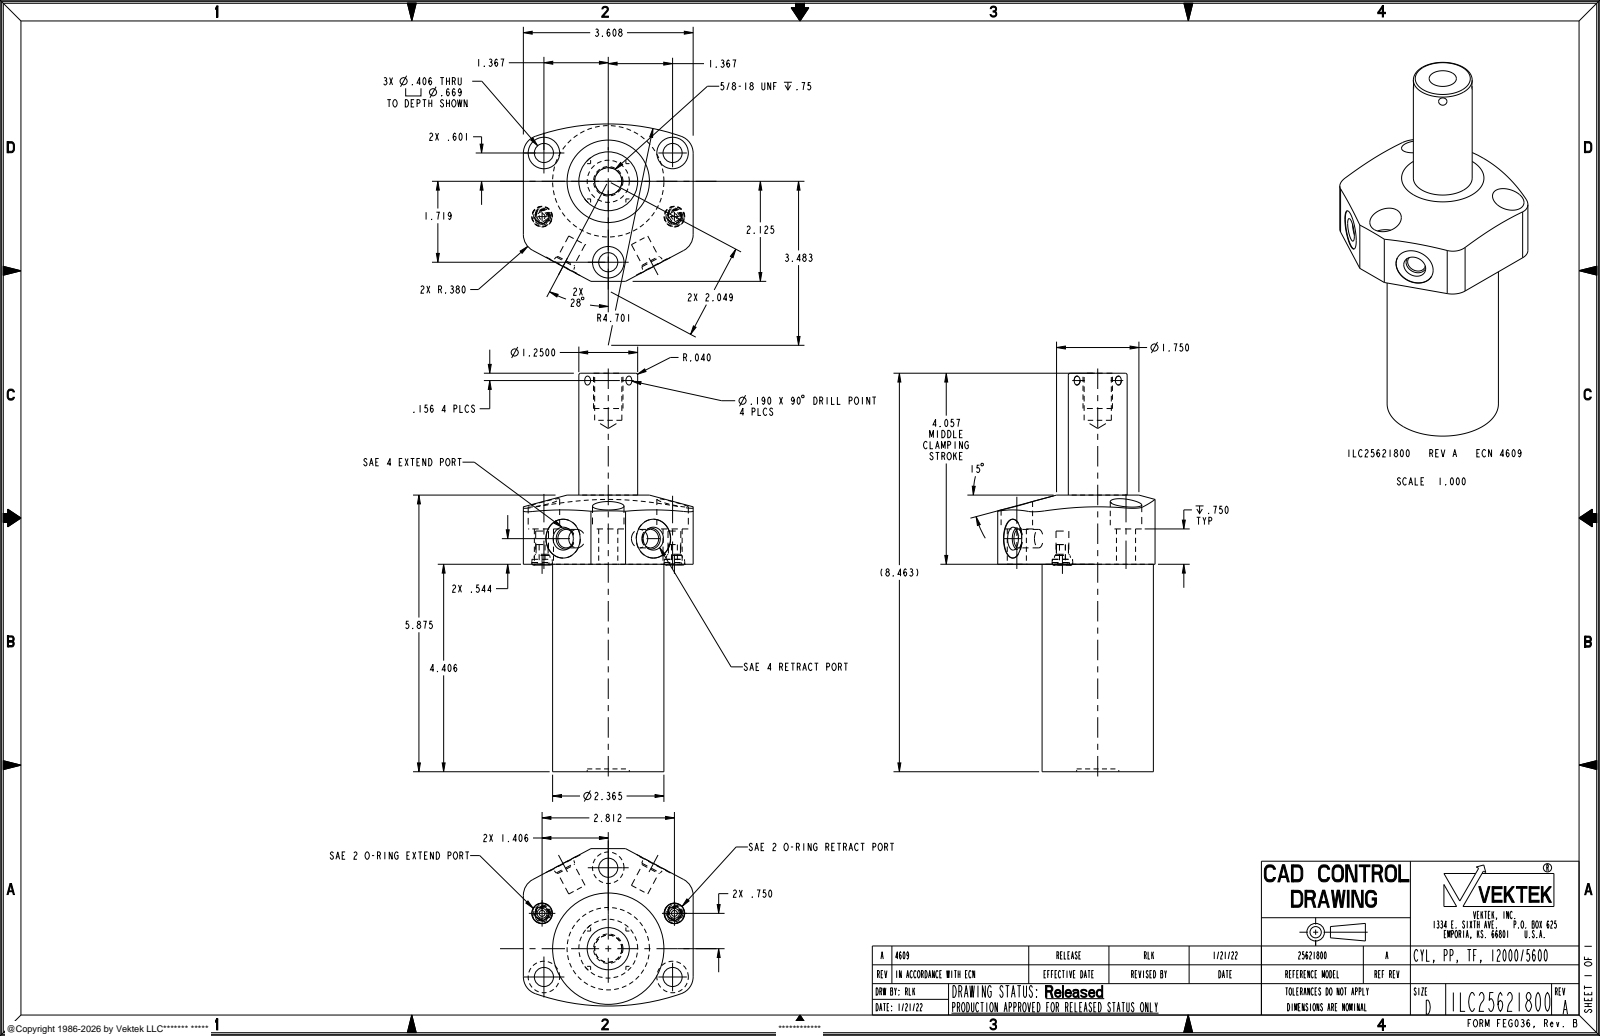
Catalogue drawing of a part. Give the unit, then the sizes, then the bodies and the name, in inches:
Units: inches
Overall size (bounding box): 8.463 × 3.808 × 3.543
Round holes (diameter × count): ⌀0.406 ×3, ⌀0.669 ×3, ⌀0.125 ×2, ⌀0.272 ×2, ⌀0.392 ×2, ⌀0.438 ×2, ⌀0.825 ×2, ⌀0.578 ×1, ⌀0.895 ×1
Round bosses / shafts (diameter × count): ⌀0.43 ×2, ⌀0.256 ×2, ⌀0.21 ×2, ⌀2.365 ×1, ⌀1.25 ×1, ⌀0.625 ×1
Partial cylindrical surfaces — rounded edges, fillets, slot ends (radius × count): R0.38 ×4, R4.701 ×1
Main face-to-face distances: 4.406, 3.608, 5.875, 1.469, 8.463, 4.057, 2.588, 0.75, 3.307, 5.156
Hole centre spacings: 1.352, 1.493, 1.593, 1.707, 2.693, 3.085, 1.719, 2.734
Volume: 35.26 in³ · Surface area: 91.9 in²
Bodies: 1 solid, 129 faces (32 planar, 59 cylindrical, 38 other)
Part name (STEP PRODUCT): ILC25621800
STEP written by: CREO PARAMETRIC BY PTC INC, 2021164 (AUTOMOTIVE_DESIGN)
